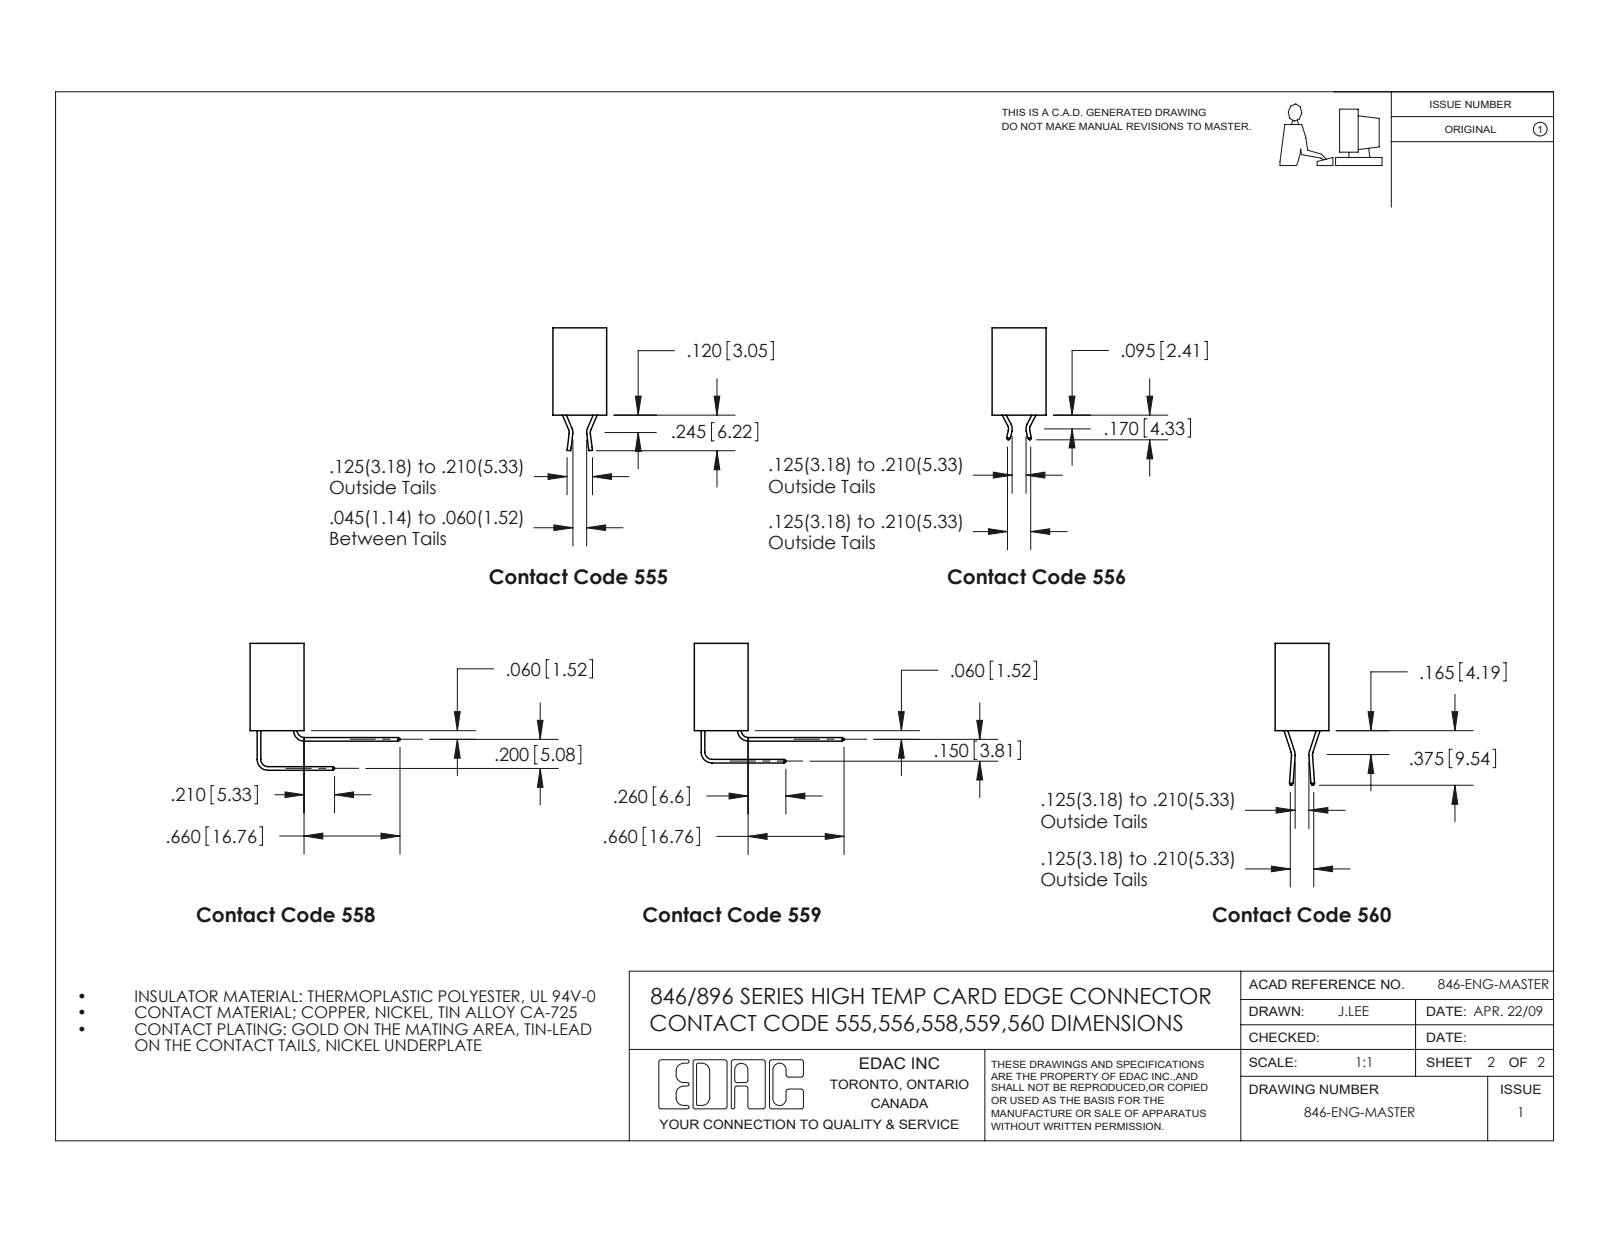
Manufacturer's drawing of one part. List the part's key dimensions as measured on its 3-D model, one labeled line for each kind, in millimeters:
Part name (STEP PRODUCT): 346 Part_0.170 Offset - 0.128 Dia; 346-005-541-602; 345-292-001_345-293-141
STEP written by: SolidWorks 2016 (CONFIG_CONTROL_DESIGN)
Units: millimetres
Bodies: 6 solids, 416 faces (280 planar, 136 cylindrical, 0 other)
Overall size (bounding box): 36.4 × 34.3 × 9.4
Volume: 3 060 mm³ · Surface area: 3 412 mm²
Round holes (diameter × count): ⌀3.3 ×2, ⌀1.6 ×1
Partial cylindrical surfaces — rounded edges, fillets, slot ends (radius × count): R0.3 ×22, R0.2 ×10, R0.3 ×10, R0.2 ×6, R0.8 ×6, R0.7 ×3, R0.8 ×2, R1 ×2
Main face-to-face distances: 6.4, 9.4, 1.2, 8.2, 1.8, 7.6, 0.6, 3.8, 5.6, 2.5
Hole centre spacings: 6.2, 24.6, 29.7
